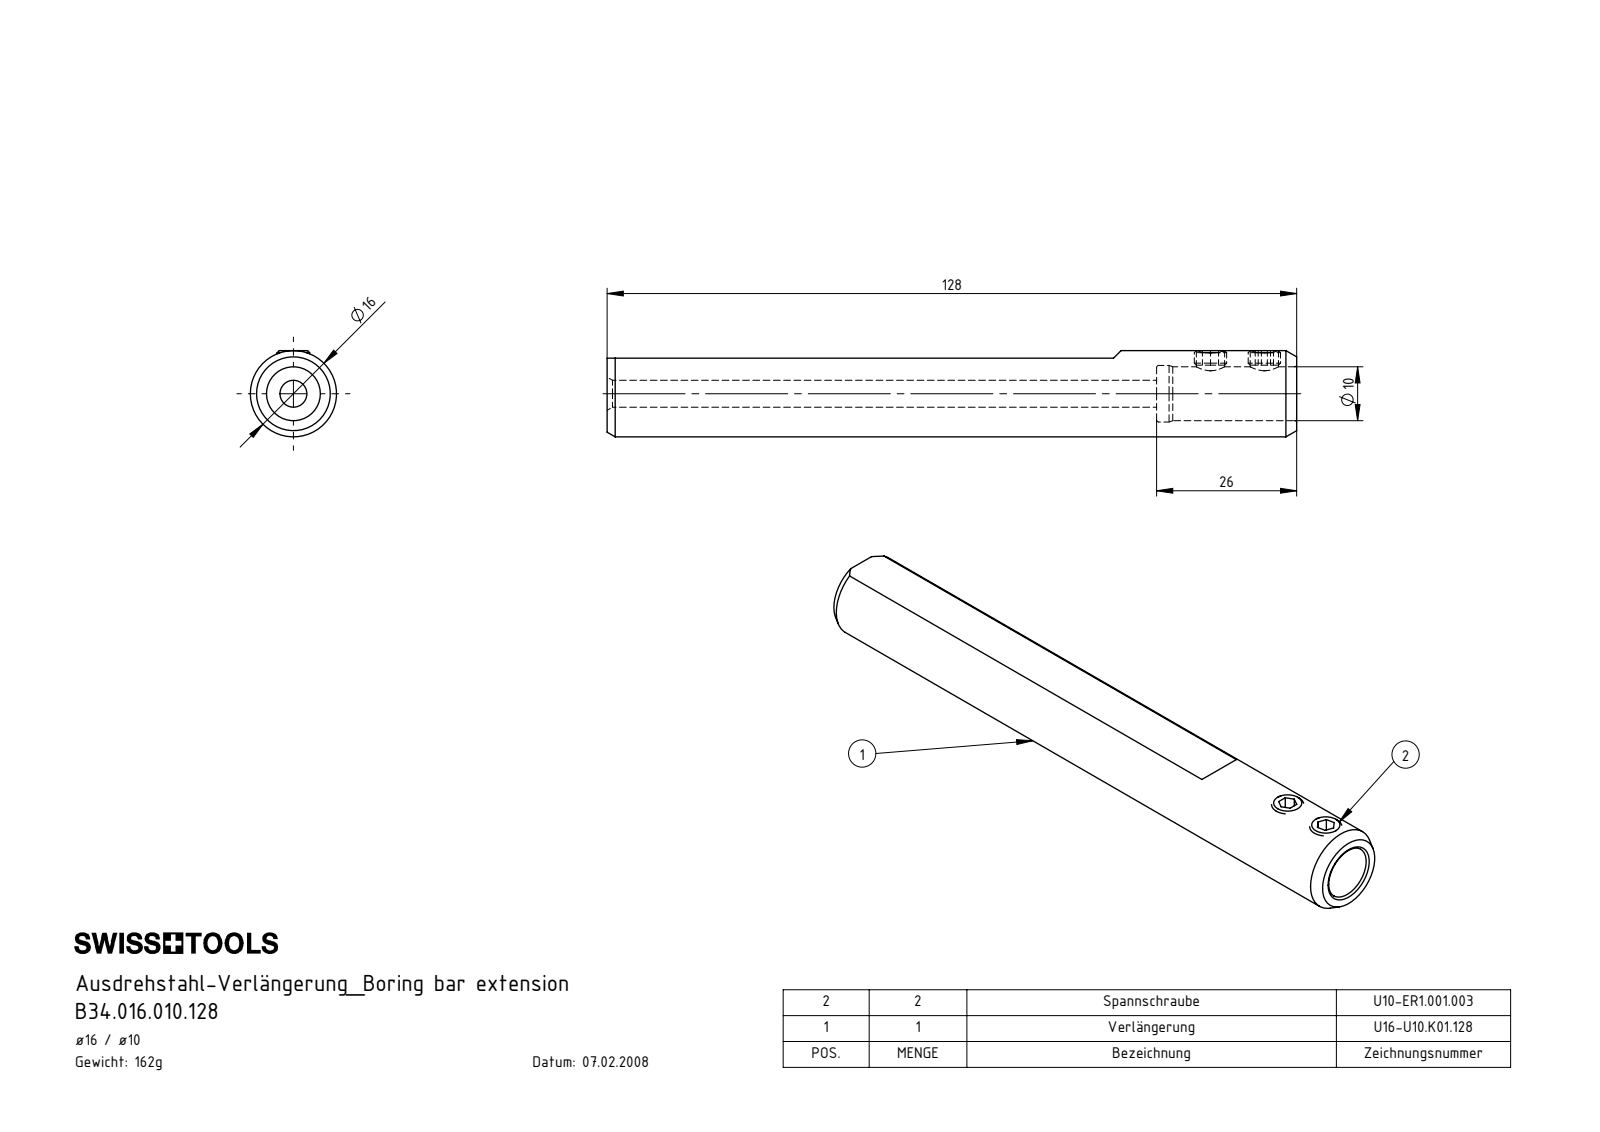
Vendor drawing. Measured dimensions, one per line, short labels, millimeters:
name: U16-U10.K01.128_A; U10-ER1.001.003_A; U16-U10.K01.128
written by: SolidWorks 2017 (CONFIG_CONTROL_DESIGN)
unit: mm
bodies: 3 solids, 58 faces (21 planar, 16 cylindrical, 21 other)
size: 128 × 16 × 16
volume: 20 743 mm³; area: 9 316 mm²
holes: 2× ⌀5.25, 1× ⌀5, 1× ⌀10, 1× ⌀10.5
bosses: 2× ⌀6, 1× ⌀16
face distances: 128, 102, 26, 3, 1.3, 2.7, 1.4, 113.5, 11.5, 14.5
hole spacings: 10
